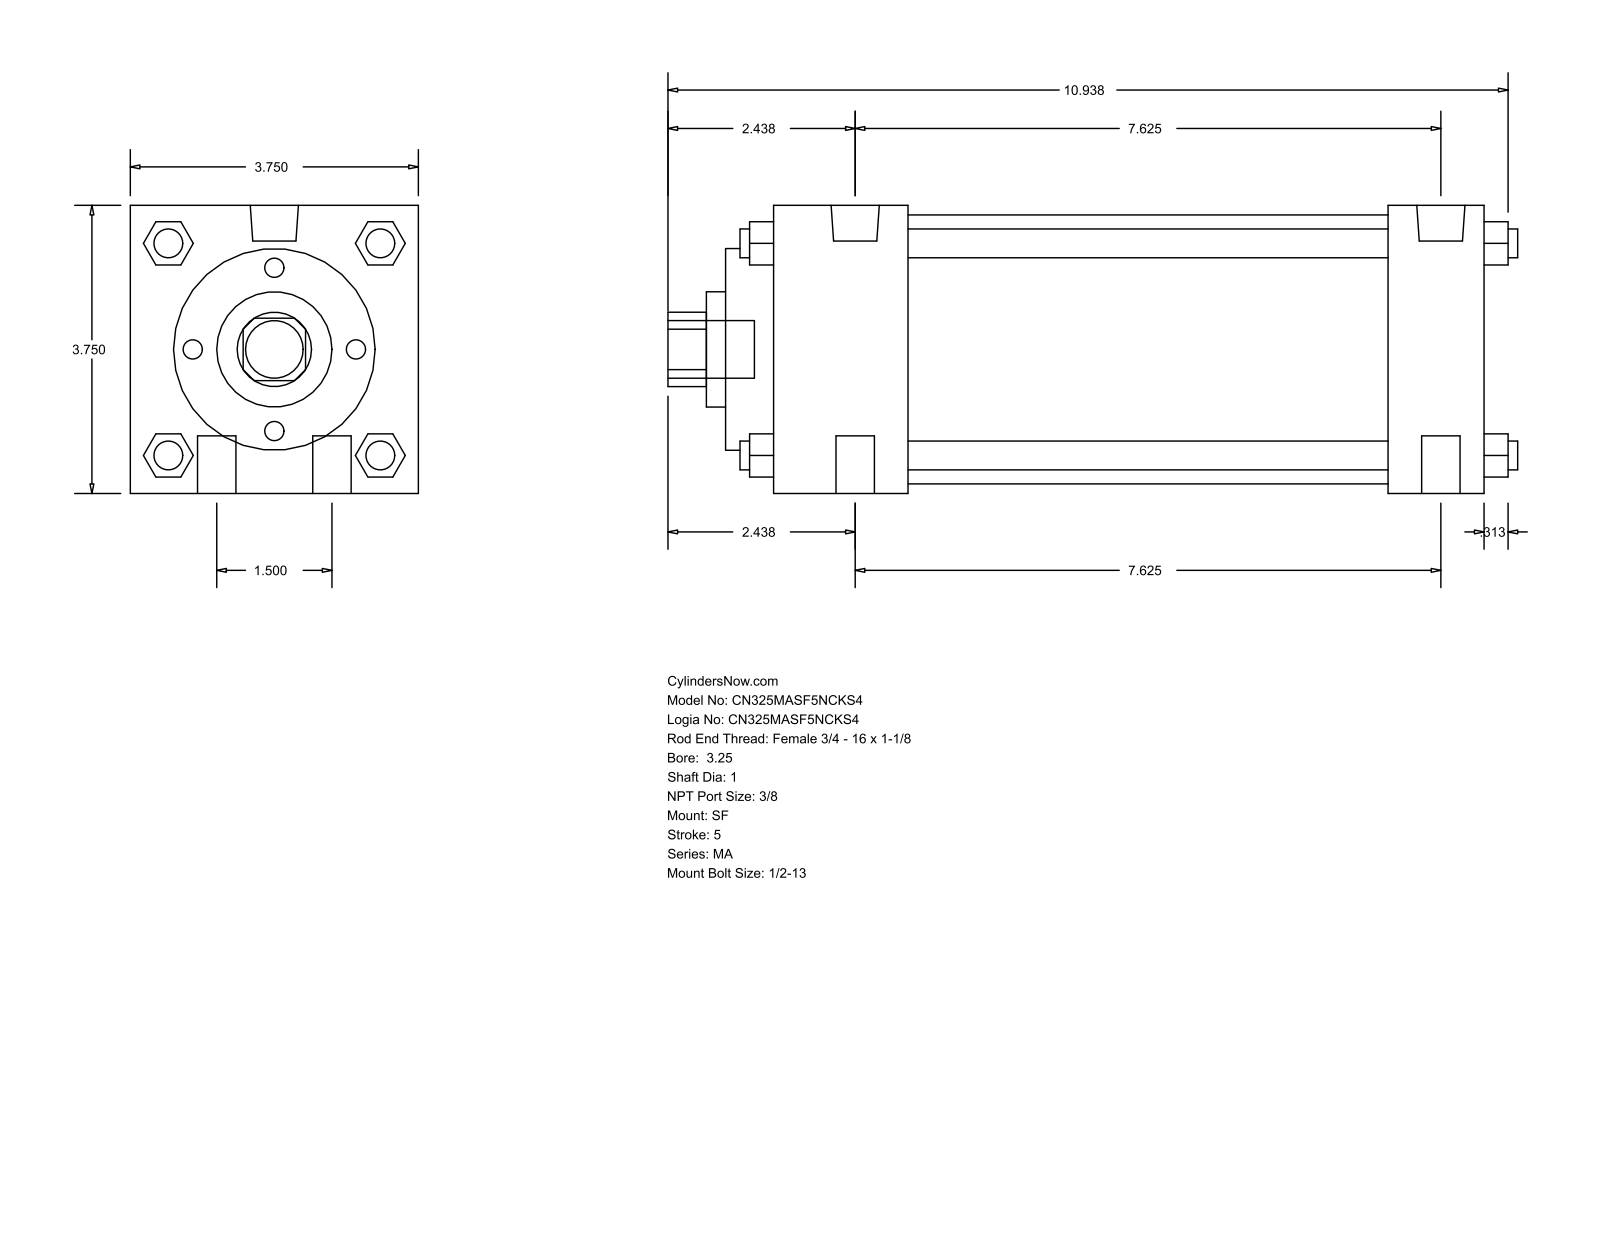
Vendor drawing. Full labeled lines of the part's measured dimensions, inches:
Part name (STEP PRODUCT): MA_SF__0325_1
STEP written by: GSSL Pune (CONFIG_CONTROL_DESIGN)
Units: inches
Bodies: 0 solids, 126 faces (95 planar, 31 cylindrical, 0 other)
Overall size (bounding box): 11.063 × 3.75 × 3.75
Round holes (diameter × count): ⌀1 ×1, ⌀1.5 ×1, ⌀2.625 ×1, ⌀3.5 ×1
Round bosses / shafts (diameter × count): ⌀0.5 ×4, ⌀0.375 ×4, ⌀0.627 ×2, ⌀0.437 ×2, ⌀0.75 ×1
Partial cylindrical surfaces — rounded edges, fillets, slot ends (radius × count): R0.484 ×1
Main face-to-face distances: 3.75, 9.25, 0.625, 8, 1.25, 1.75, 6.25, 7.5, 2.375, 8.625
